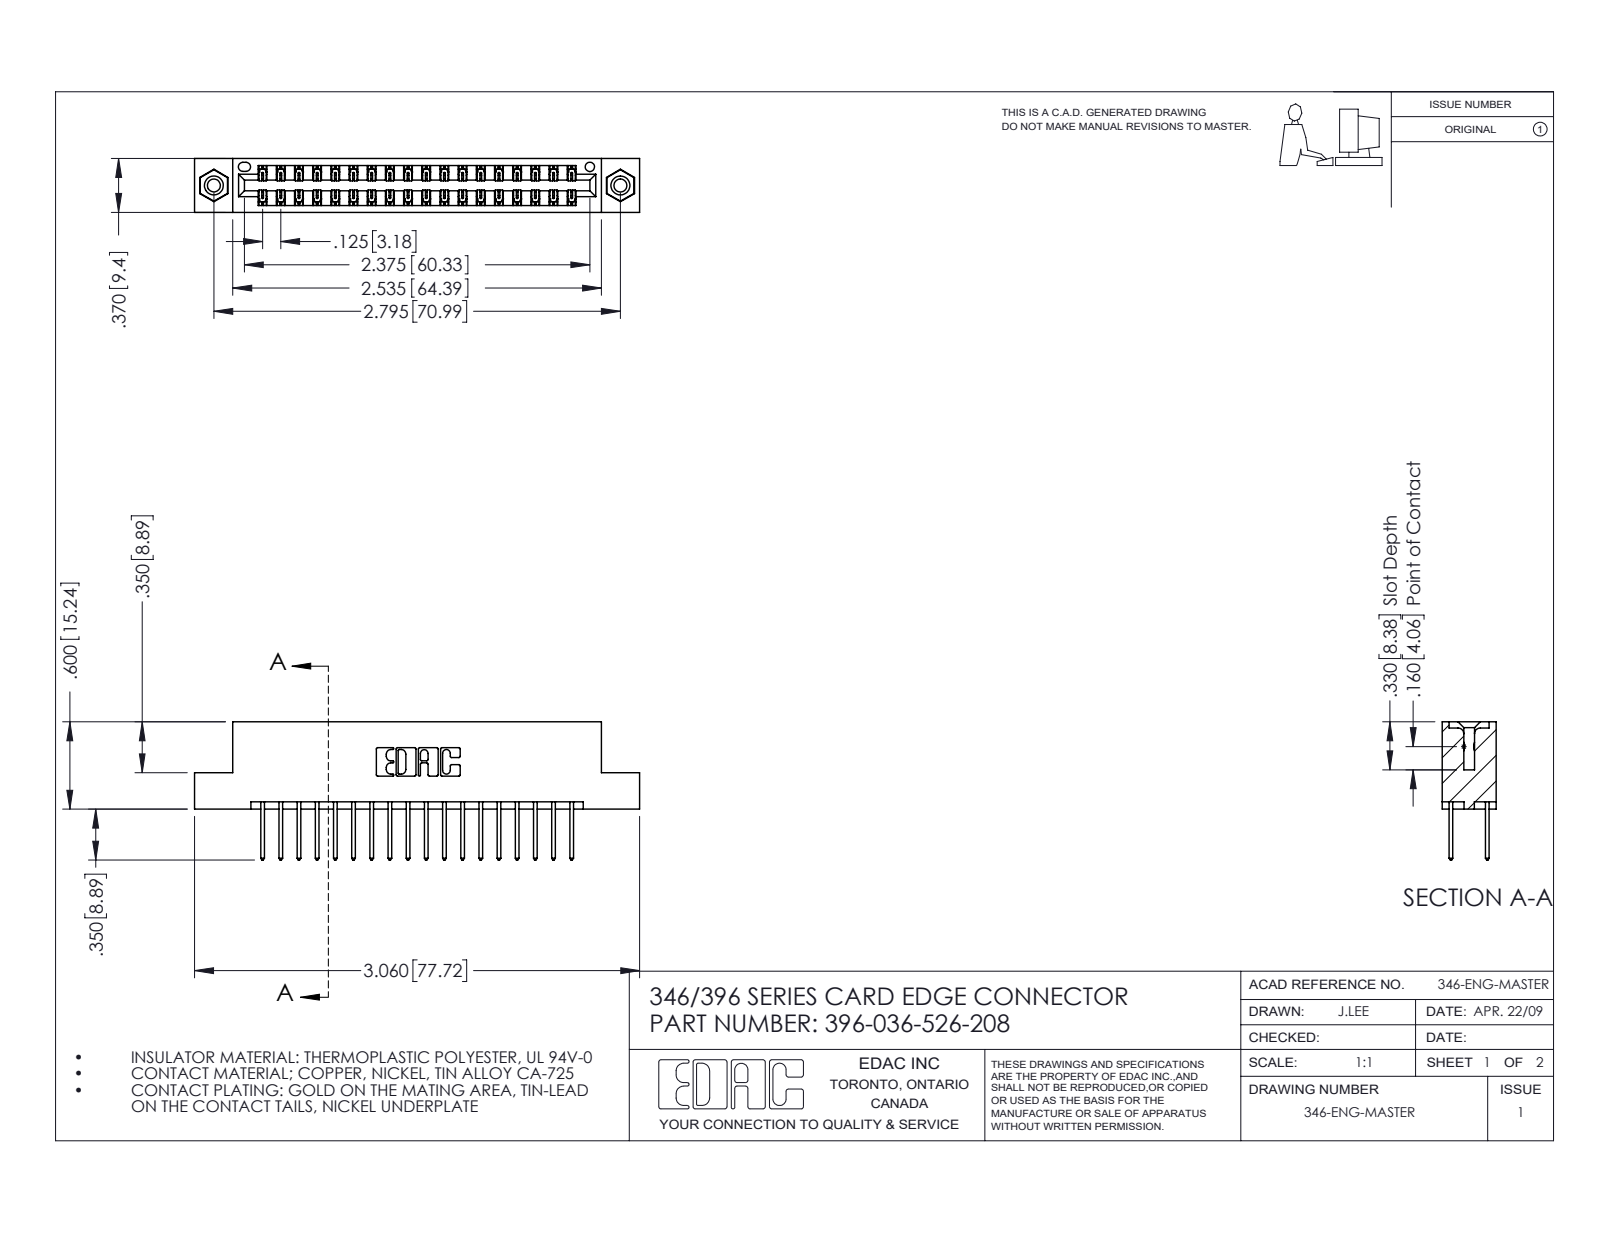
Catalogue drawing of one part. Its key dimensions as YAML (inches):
part_name: "345-292-001_345-293-126; 396-036-526-208; 345-250-001_345-250-003-102; 346 Part_Flush Mounting Lugs - 0.156 Dia-TI"
step_written_by: "SolidWorks 2016 (CONFIG_CONTROL_DESIGN)"
units: inches
bodies: {solids: 39, faces: 2054, planar: 1368, cylindrical: 670, other: 16}
overall_size: [3.06, 0.95, 0.37]
volume: 0.454
surface_area: 15.72
round_holes:
  - {diameter: 0.089, count: 2}
  - {diameter: 0.125, count: 2}
  - {diameter: 0.156, count: 2}
  - {diameter: 0.064, count: 1}
round_bosses_or_shafts:
  - {diameter: 0.155, count: 2}
partial_cylinders:
  - {radius: 0.006, count: 54}
  - {radius: 0.01, count: 36}
  - {radius: 0.01, count: 22}
  - {radius: 0.007, count: 6}
  - {radius: 0.031, count: 6}
  - {radius: 0.026, count: 3}
  - {radius: 0.014, count: 2}
  - {radius: 0.022, count: 2}
face_to_face_distances: [0.048, 0.322, 0.25, 0.37, 0.072, 0.298, 0.025, 0.275, 0.148, 0.222]
hole_center_spacings: [0.246, 2.588, 2.795]
